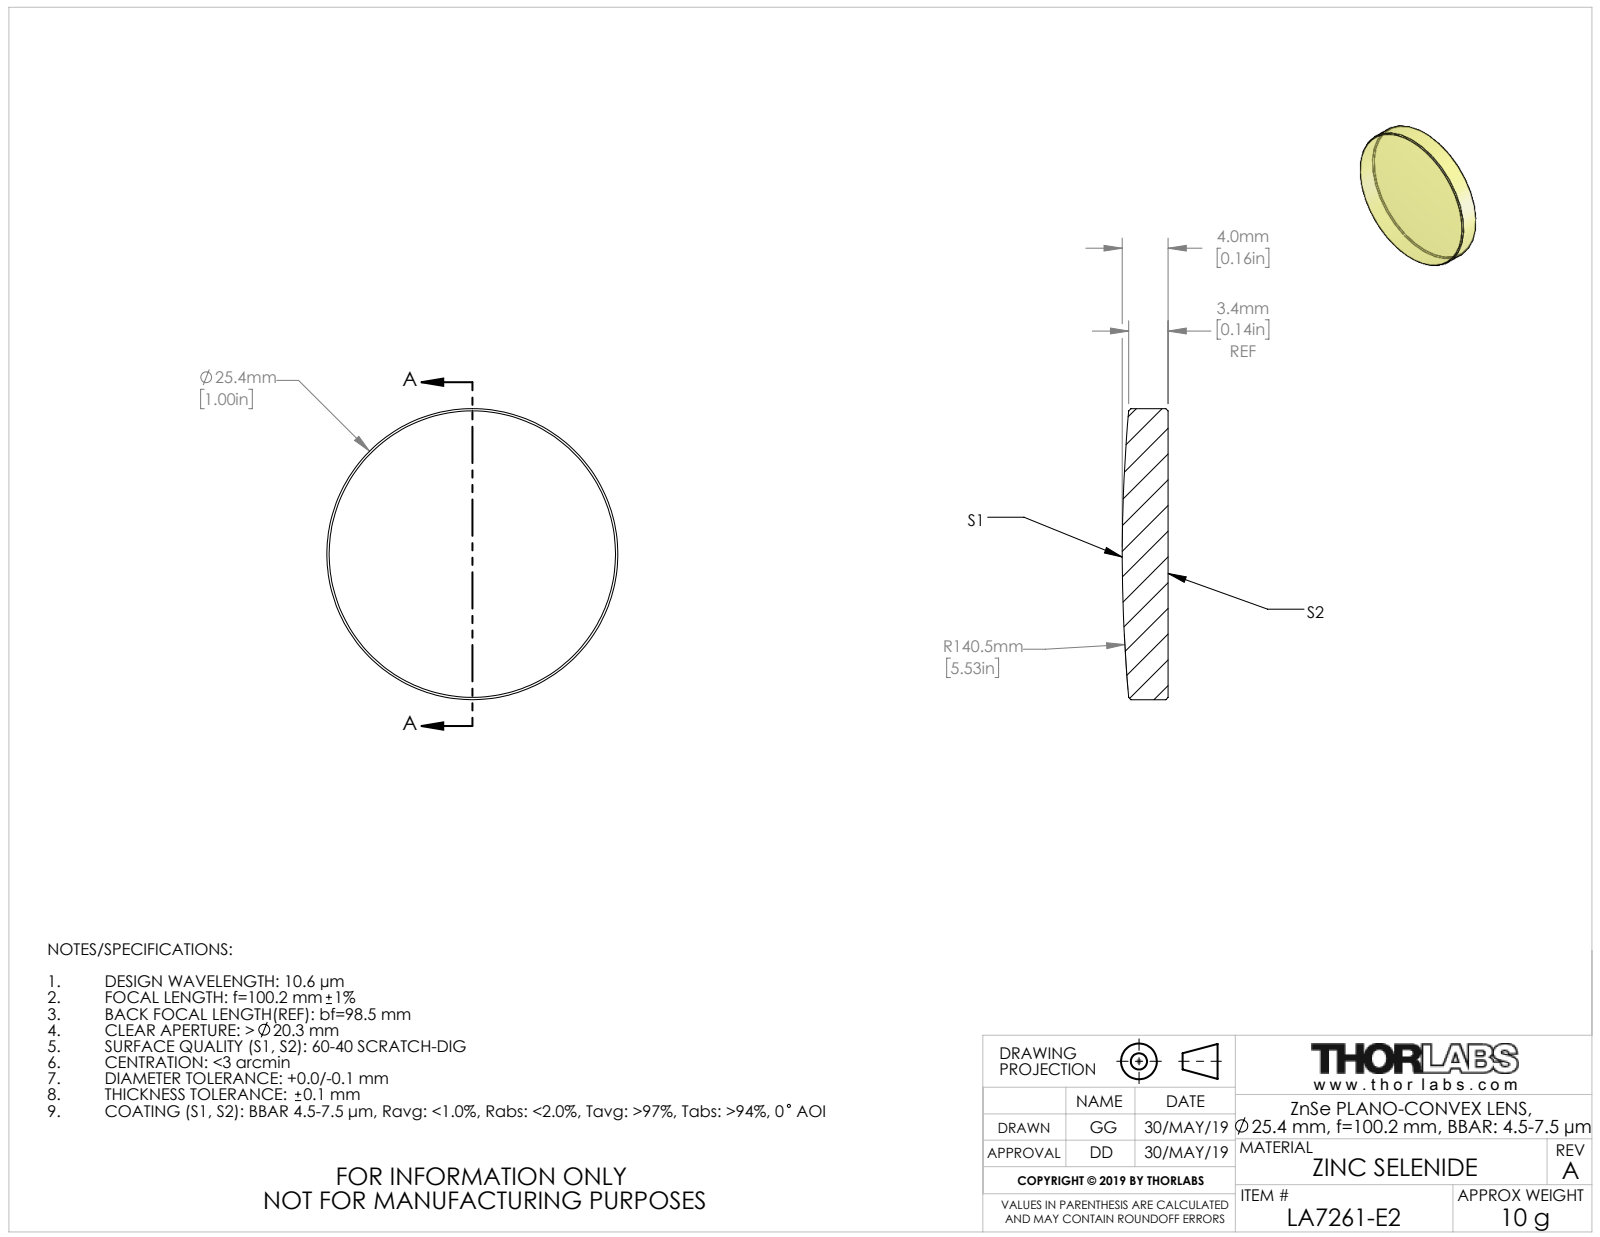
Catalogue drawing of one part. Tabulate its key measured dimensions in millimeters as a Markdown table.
| quantity | value |
| --- | --- |
| part name | TTN047597-E0W |
| STEP written by | SolidWorks 2018 (CONFIG_CONTROL_DESIGN) |
| units | millimeters |
| bodies | 1 solid, 9 faces (1 planar, 2 cylindrical, 6 other) |
| overall size | 25.4 × 25.4 × 4 |
| volume | 1 878 mm³ |
| surface area | 1 270 mm² |
| round bosses / shafts (diameter × count) | 25.4 × 1 |
